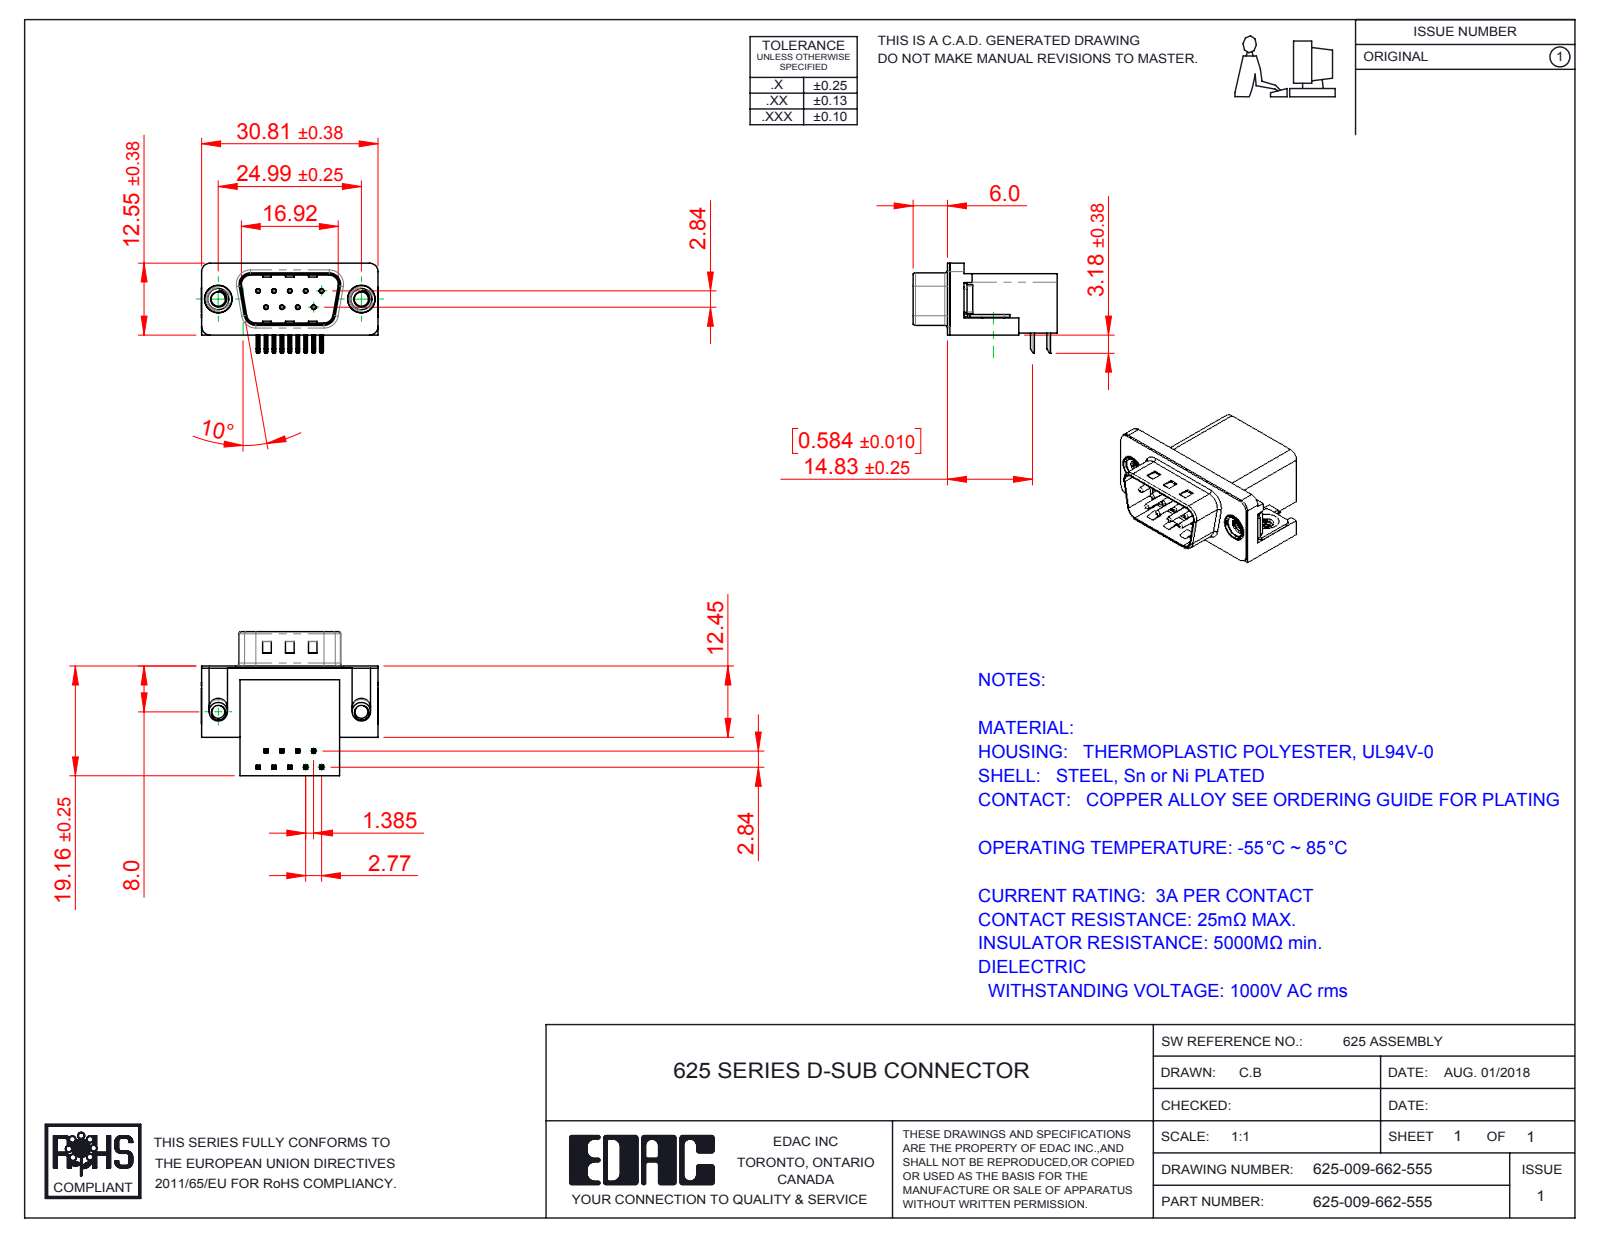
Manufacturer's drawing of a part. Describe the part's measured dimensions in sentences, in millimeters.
The part is named "625 Housing_9 Socket; 625 Shell_9 Socket; 625 4-40 Threaded Board Mount; 625 Contact Top (+3 more)". Its 3-D file was written by "SolidWorks 2016 (CONFIG_CONTROL_DESIGN)". It is 15 solids with 1025 faces: 575 planar, 333 cylindrical and 117 other. Overall it measures 30.89 by 25.16 by 15.73 millimeters. Its volume is 4 481 cubic millimeters and its surface area 5 034 square millimeters. Round holes: 9 of diameter 0.35, 9 of diameter 0.8, 2 of diameter 2.26, 2 of diameter 2.5, 2 of diameter 4, 2 of diameter 4.8, 2 of diameter 5. Round bosses or shafts: 9 of diameter 0.75, 2 of diameter 4.9, 2 of diameter 4.75, 2 of diameter 3.9, 2 of diameter 3.26. Partial cylindrical surfaces (rounded edges, fillets, slot ends): 44 of radius 0.25, 18 of radius 0.12, 16 of radius 1, 9 of radius 0.5, 8 of radius 1.5, 8 of radius 1.6, 4 of radius 0.9, 4 of radius 2. The main face-to-face distances are 0.4, 10.34, 18.76, 19.16, 2.9, 16.26, 2.5, 0.35, 10.69, 6.7. The hole center spacings are 3.16, 2.77, 5.54, 5.03, 5.04, 8.31, 7.48, 7.49.
